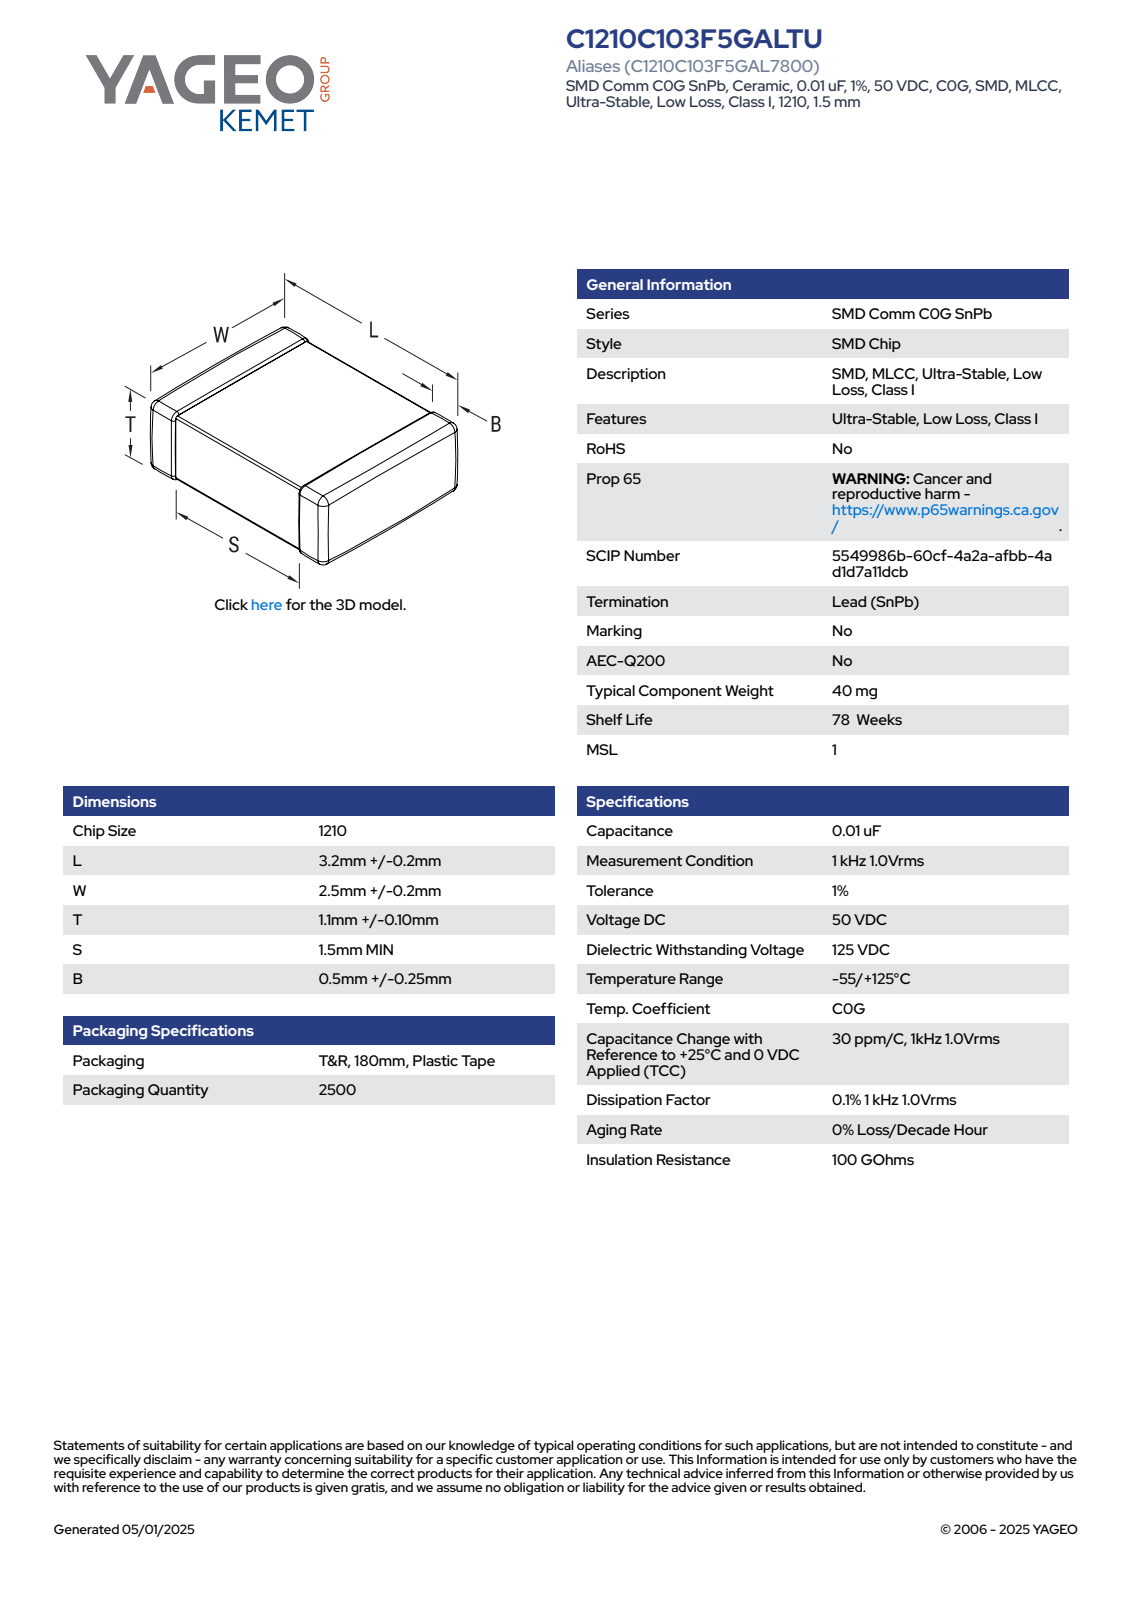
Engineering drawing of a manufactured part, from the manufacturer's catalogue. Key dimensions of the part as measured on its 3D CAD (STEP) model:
Part name (STEP PRODUCT): CCS_CCSTD_1210_L3.4W2.7T1.2B0.5
STEP written by: SolidWorks 2021 (AUTOMOTIVE_DESIGN)
Units: millimetres
Bodies: 4 solids, 125 faces (71 planar, 38 cylindrical, 16 other)
Overall size (bounding box): 3.4 × 2.7 × 1.2
Volume: 10 mm³ · Surface area: 33 mm²
Main face-to-face distances: 1.14, 1.08, 1.2, 3.4, 2.64, 2.58, 2.7, 1.15, 1.09, 0.4
